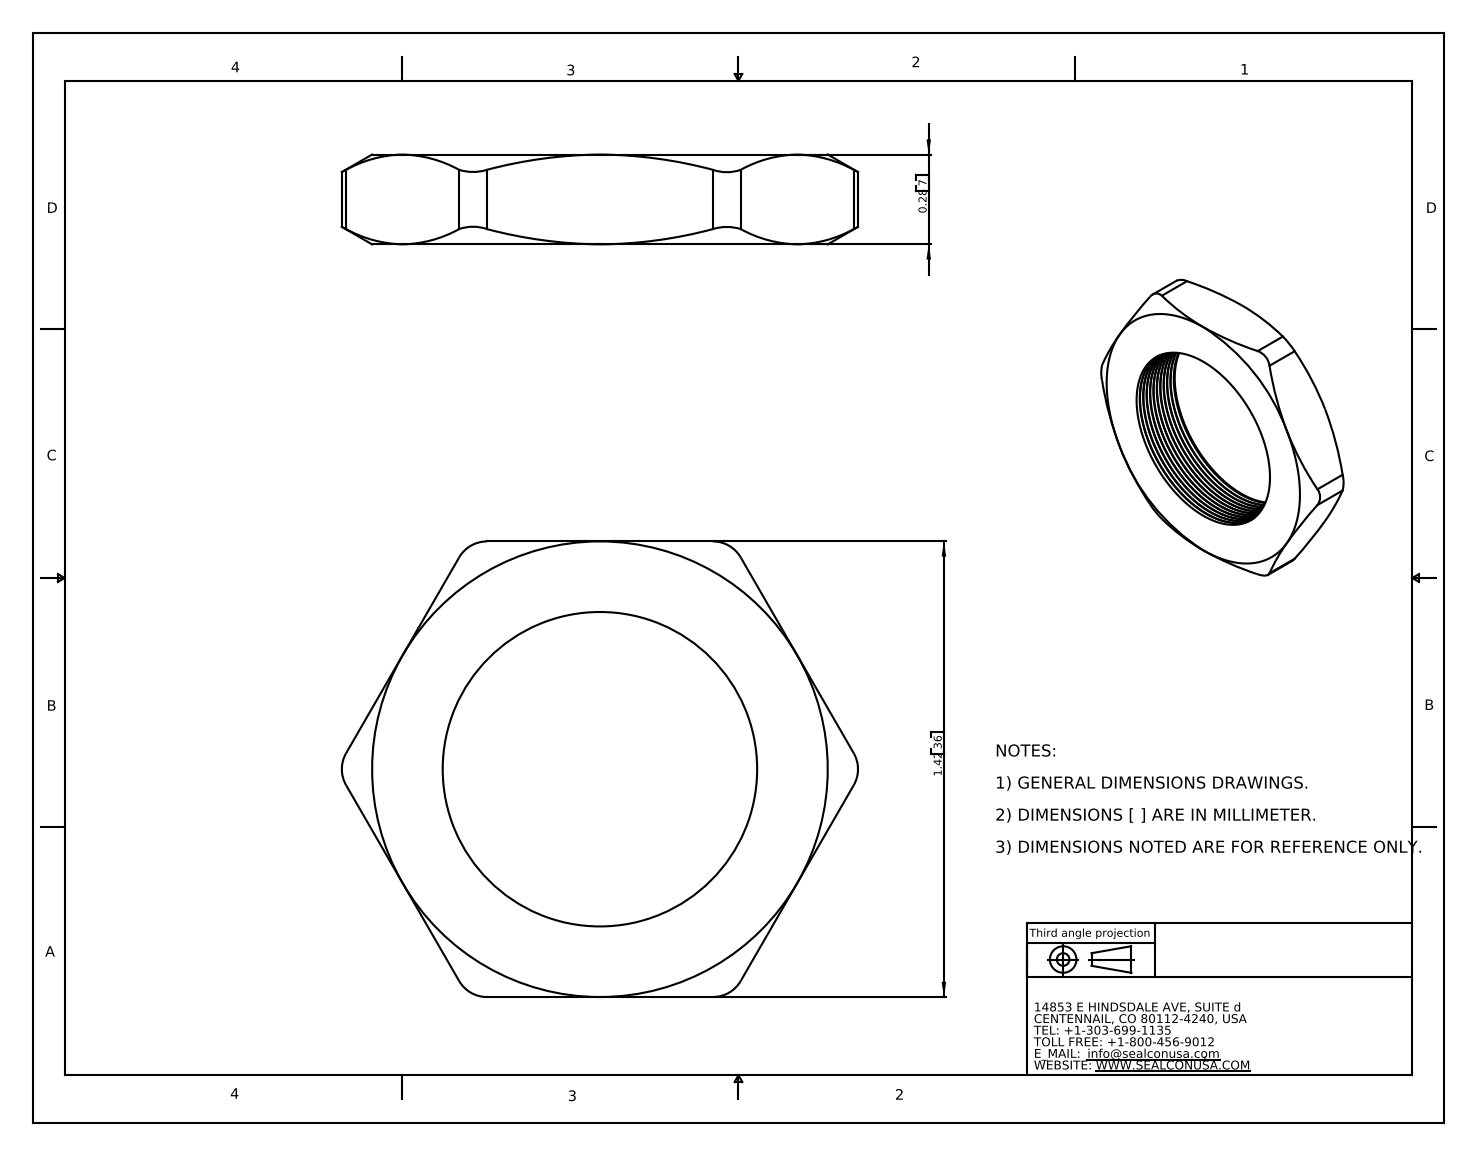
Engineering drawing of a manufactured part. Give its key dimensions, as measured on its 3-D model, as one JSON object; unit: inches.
{"part_name": "NM-25", "step_written_by": "SolidWorks 2007 (CONFIG_CONTROL_DESIGN)", "units": "inches", "bodies": {"solids": 1, "faces": 95, "planar": 8, "cylindrical": 29, "other": 58}, "overall_size": [1.609, 1.42, 0.28], "volume_in3": 0.263, "surface_area_in2": 4.859, "round_holes": [[0.98, 1]], "partial_cylinders_radius": [[0.1, 6]], "face_to_face_distances": [0.28, 1.42]}
